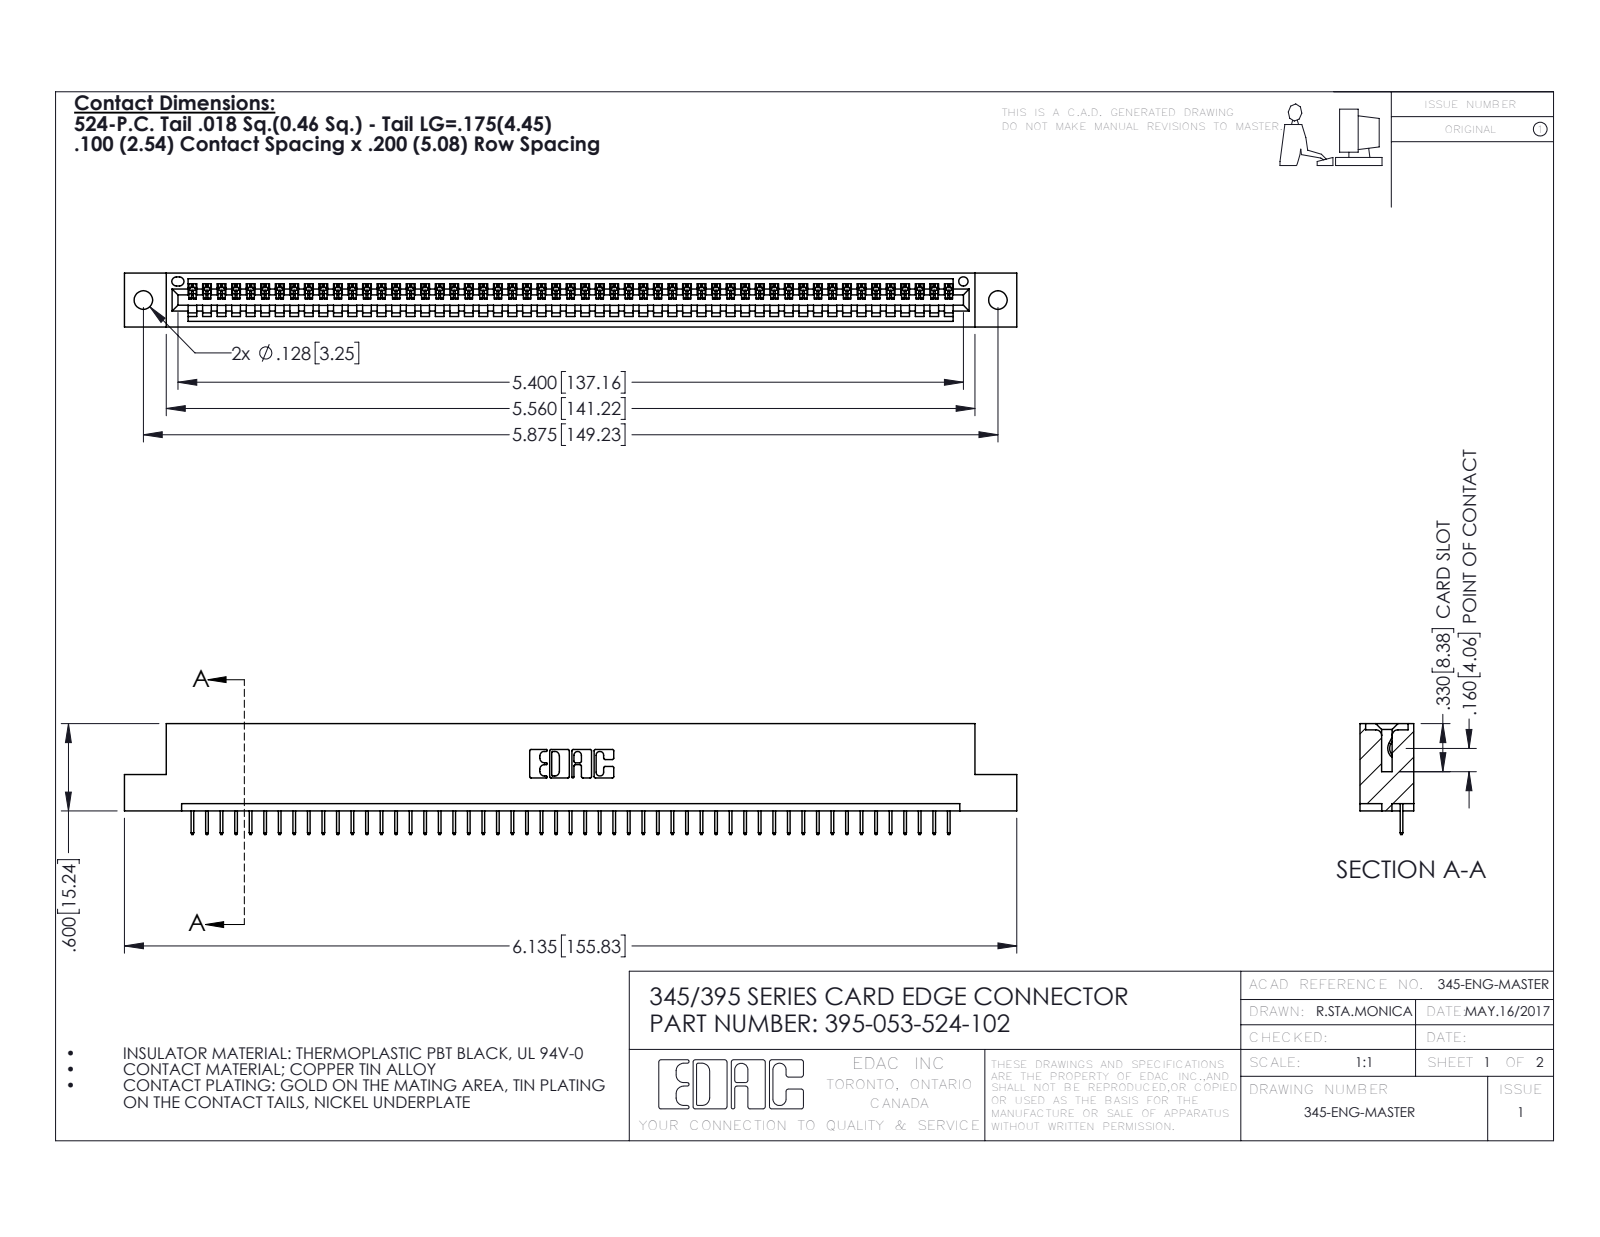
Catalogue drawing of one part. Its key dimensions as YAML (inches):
part_name: "345 Part_Flush Mounting Lugs - 0.128 Dia; 395-053-524-102; 345-292-001_345-293-124"
step_written_by: "SolidWorks 2016 (CONFIG_CONTROL_DESIGN)"
units: inches
bodies: {solids: 54, faces: 3412, planar: 2518, cylindrical: 894, other: 0}
overall_size: [6.135, 0.762, 0.37]
volume: 0.894
surface_area: 28.94
round_holes:
  - {diameter: 0.128, count: 2}
  - {diameter: 0.064, count: 1}
partial_cylinders:
  - {radius: 0.006, count: 106}
  - {radius: 0.01, count: 22}
  - {radius: 0.007, count: 6}
  - {radius: 0.031, count: 6}
  - {radius: 0.026, count: 3}
  - {radius: 0.031, count: 2}
  - {radius: 0.04, count: 2}
  - {radius: 0.014, count: 1}
face_to_face_distances: [0.298, 0.072, 0.37, 0.2, 0.098, 0.272, 0.025, 0.225, 0.072, 0.149]
hole_center_spacings: [0.27, 5.639, 5.875]
